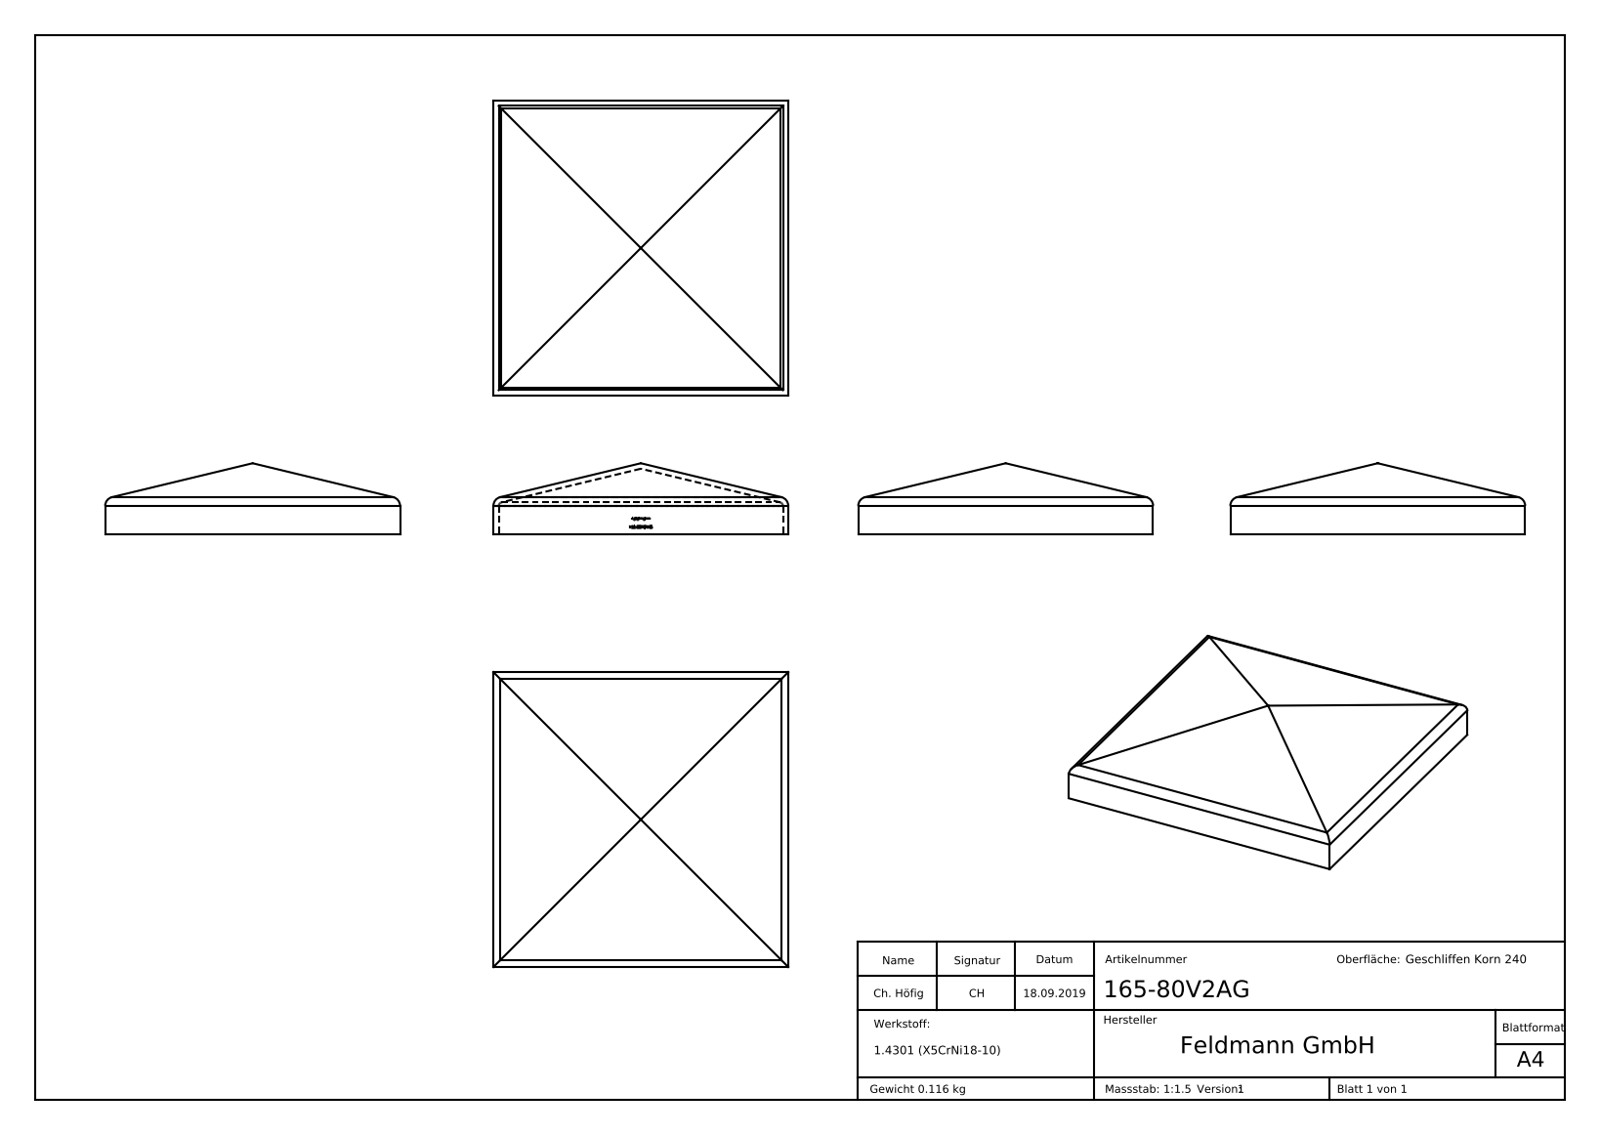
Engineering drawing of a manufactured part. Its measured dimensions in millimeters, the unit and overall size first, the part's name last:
Units: millimetres
Overall size (bounding box): 83 × 83 × 20
Partial cylindrical surfaces — rounded edges, fillets, slot ends (radius × count): R1 ×4, R2.5 ×4, R0.1 ×2
Main face-to-face distances: 1.5, 81.5, 83, 80, 1.4, 80.1, 81.6, 0.45, 1.66, 1.78
Volume: 14 643 mm³ · Surface area: 20 026 mm²
Bodies: 1 solid, 262 faces (144 planar, 12 cylindrical, 106 other)
Part name (STEP PRODUCT): 165-80V2AG
STEP written by: SolidWorks 2015 (CONFIG_CONTROL_DESIGN)
